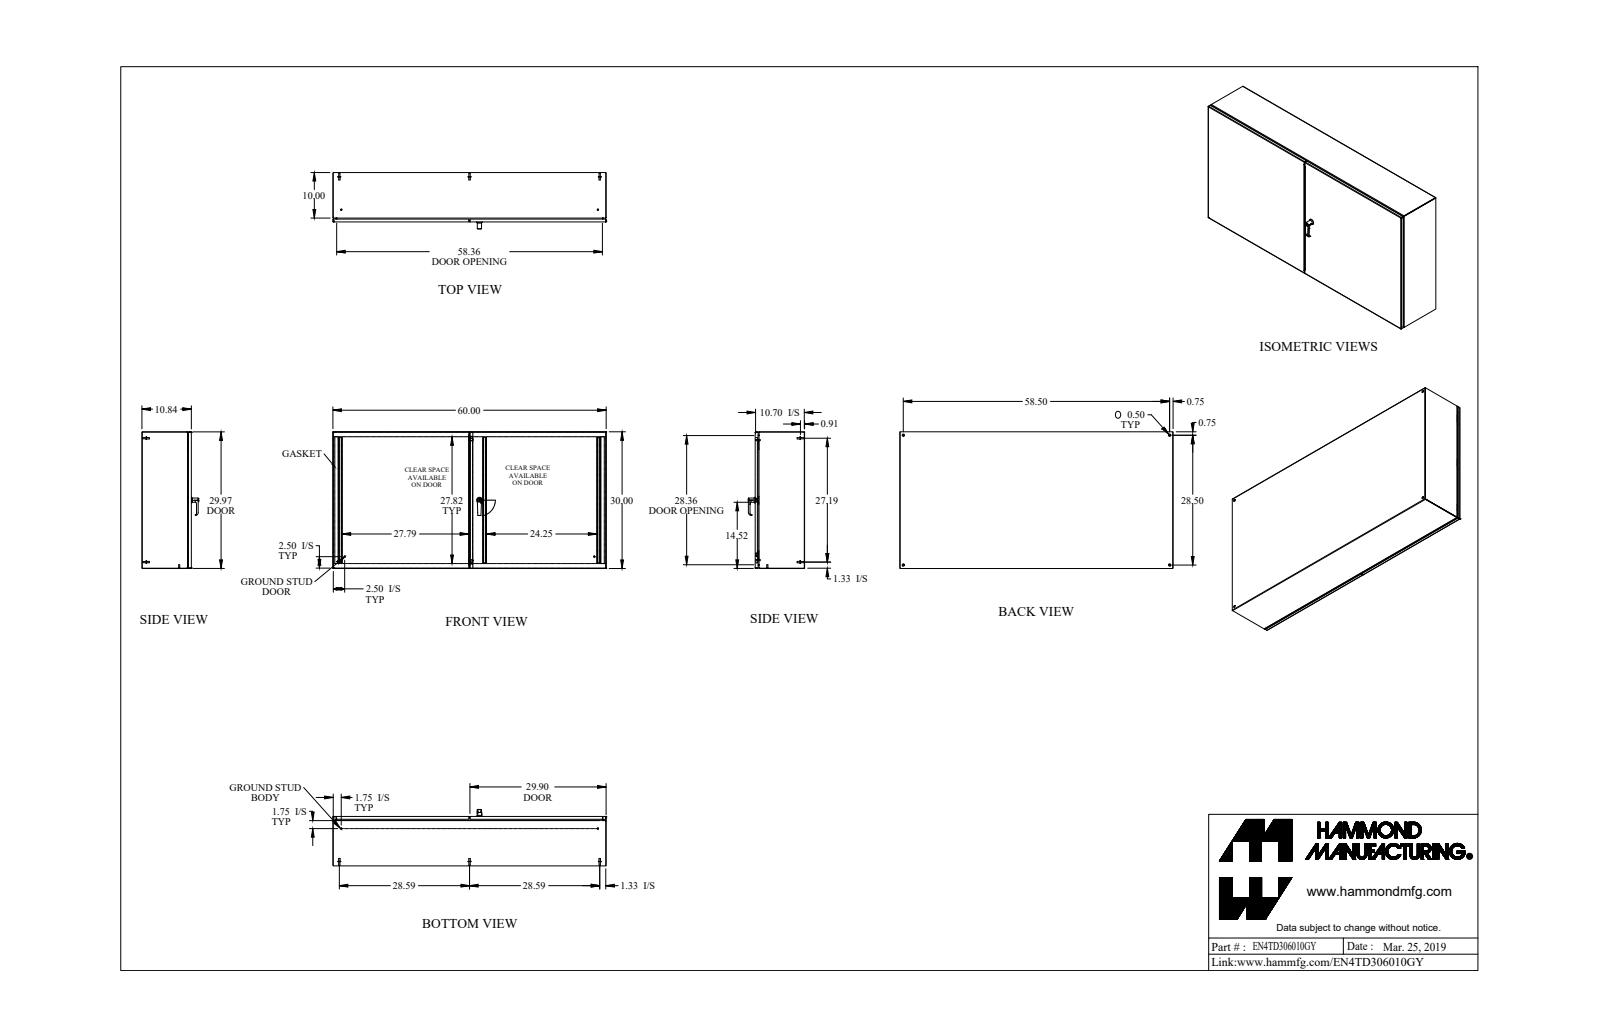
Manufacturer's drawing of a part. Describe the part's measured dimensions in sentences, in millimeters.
The part is named "EN4TD306010GY". Its 3-D file was written by "SolidWorks 2018 (AUTOMOTIVE_DESIGN)". It is 91 solids with 2297 faces: 1053 planar, 846 cylindrical and 398 other. Overall it measures 1524 by 762 by 314.2 millimeters. Its volume is 7 936 000 cubic millimeters and its surface area 8 341 000 square millimeters. Round holes: 5 of diameter 5, 4 of diameter 4.5, 4 of diameter 6.7, 4 of diameter 12.7, 3 of diameter 6.1, 3 of diameter 6.1, 2 of diameter 4.4, 2 of diameter 6.4, 2 of diameter 6.5, 2 of diameter 6.6, 2 of diameter 7, 2 of diameter 8. Round bosses or shafts: 10 of diameter 6.4, 8 of diameter 15.9, 6 of diameter 8, 6 of diameter 6.9, 4 of diameter 13, 4 of diameter 7.1, 4 of diameter 4, 3 of diameter 19.1. Partial cylindrical surfaces (rounded edges, fillets, slot ends): 30 of radius 1.1, 30 of radius 2.1, 26 of radius 0.9, 26 of radius 2.7, 25 of radius 1.6, 20 of radius 2.4, 16 of radius 0.5, 15 of radius 0.4. The main face-to-face distances are 1.8, 273.6, 271.7, 275.4, 760.2, 758.3, 1522.2, 762, 1520.3, 1524. The hole center spacings are 20, 335, 680.5, 723.9, 777.3, 806.4, 876.2, 1485.9.
